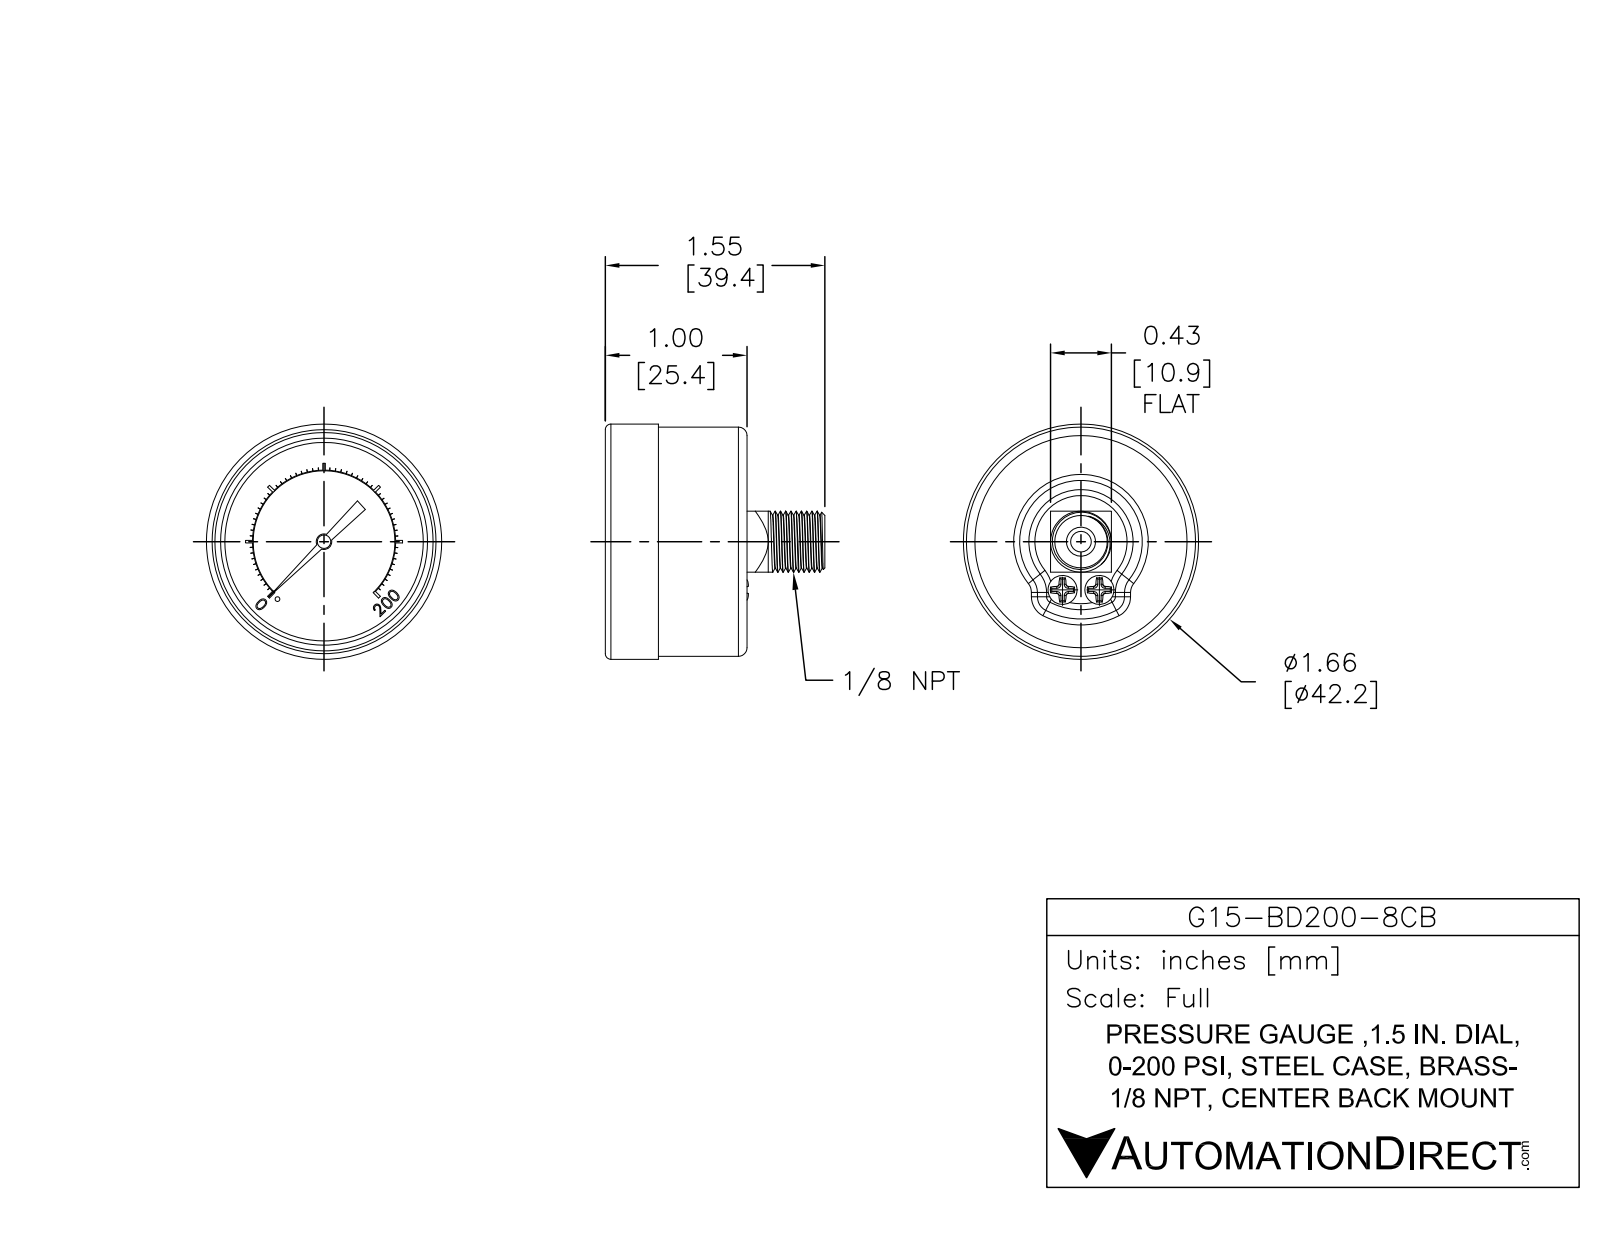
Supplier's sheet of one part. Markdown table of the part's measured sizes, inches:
| quantity | value |
| --- | --- |
| part name | G15-BD200-8CB |
| STEP written by | SolidWorks 2021 (AUTOMOTIVE_DESIGN) |
| units | inches |
| bodies | 1 solid, 425 faces (270 planar, 85 cylindrical, 70 other) |
| overall size | 1.66 × 1.66 × 1.55 |
| volume | 1.676 in³ |
| surface area | 12.02 in² |
| round holes (diameter × count) | 0.145 × 1, 1.4 × 1 |
| round bosses / shafts (diameter × count) | 0.205 × 2, 1.66 × 1, 1.617 × 1, 0.43 × 1, 0.086 × 1, 0.06 × 1, 0.033 × 1 |
| partial cylindrical surfaces (radius × count) | 0.06 × 4, 0.015 × 2, 0.048 × 1, 0.5 × 1, 0.505 × 1 |
| main face-to-face distances | 0.71, 0.43, 0.1, 0.61, 0.96, 0.86, 0.25, 0.04, 0.625, 0.525 |
